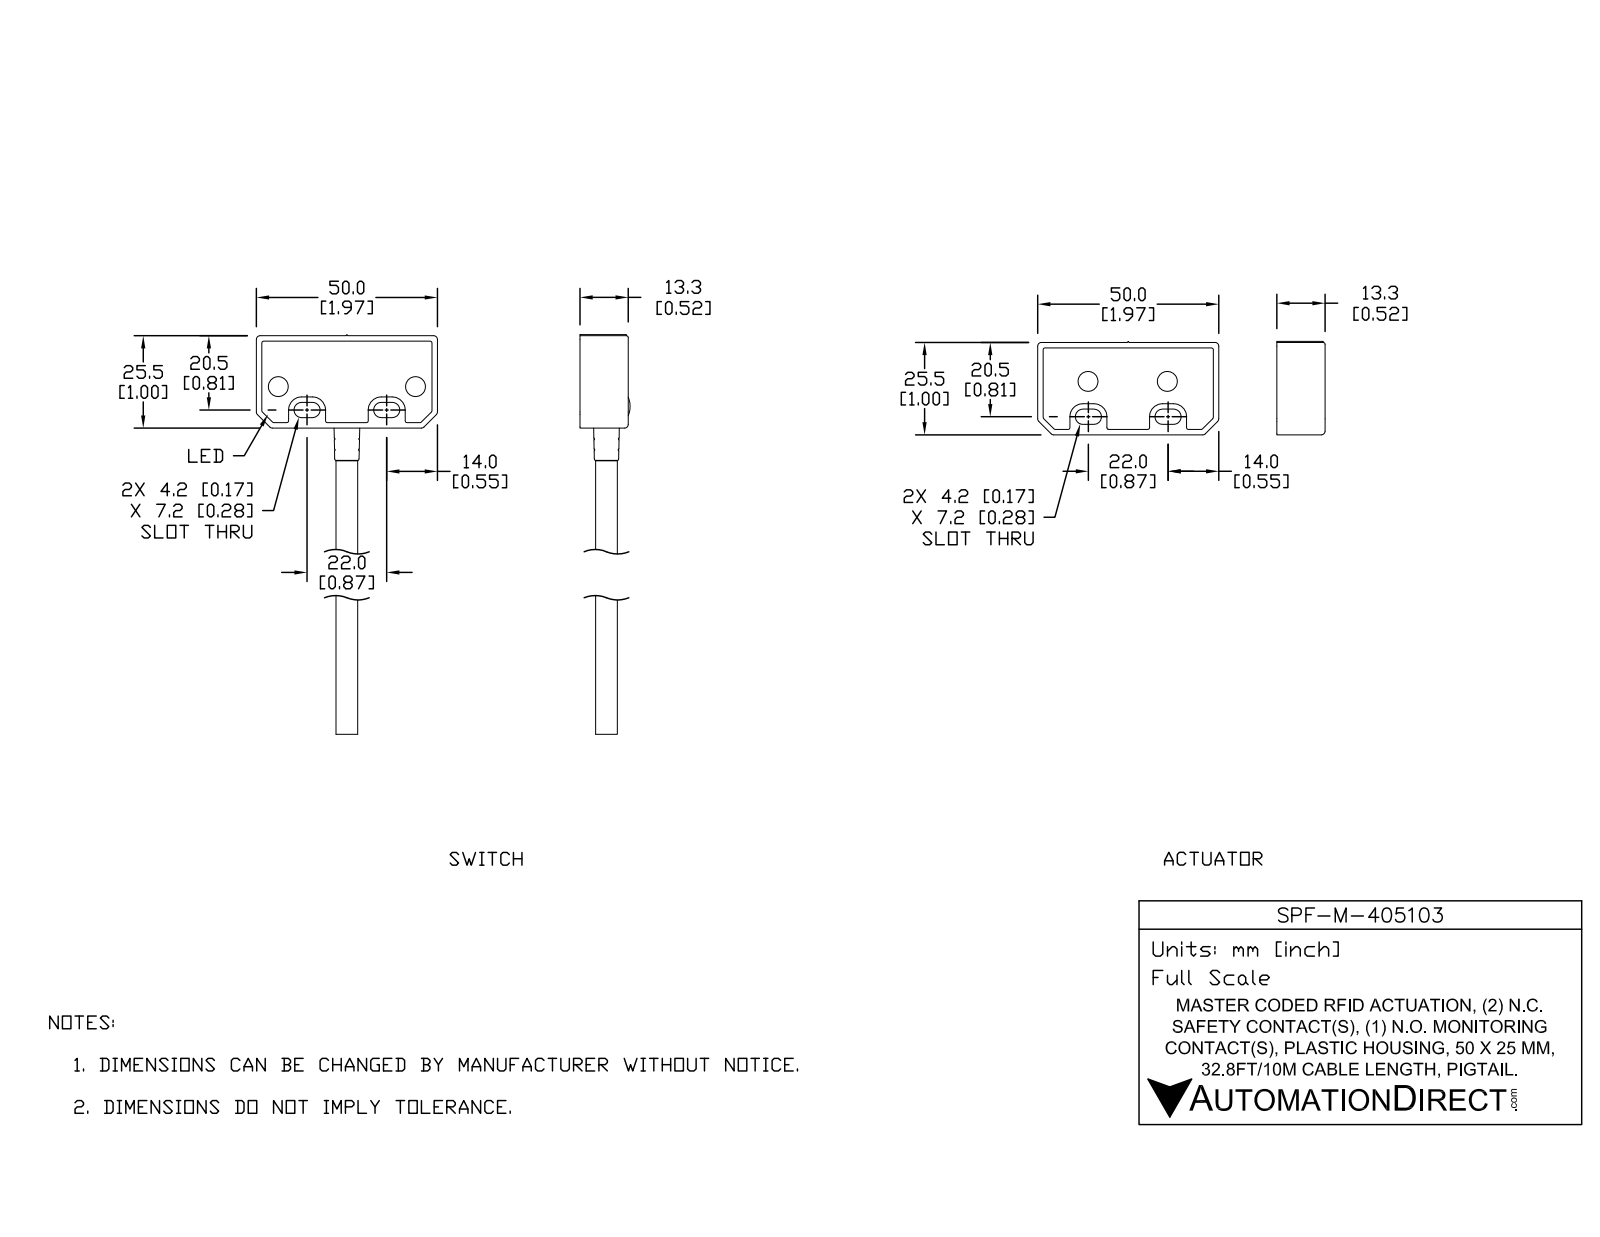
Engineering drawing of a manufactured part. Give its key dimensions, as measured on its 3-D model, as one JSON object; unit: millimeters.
{"part_name": "SPF-M-405103_2; SPF-M-405103; SPF-M-405103_1", "step_written_by": "SolidWorks 2017 (AUTOMOTIVE_DESIGN)", "units": "millimeters", "bodies": {"solids": 12, "faces": 1147, "planar": 475, "cylindrical": 358, "other": 314}, "overall_size": [205.5, 50, 13.8], "volume_mm3": 18110, "surface_area_mm2": 23430, "round_holes": [[5, 4], [3, 1], [4.4, 1], [5.4, 1], [5.9, 1], [7, 1]], "round_bosses_or_shafts": [[2, 4], [4.9, 2], [0.8, 2], [8.6, 1], [7.6, 1], [7.1, 1], [6, 1], [5.3, 1]], "partial_cylinders_radius": [[0.5, 132], [1, 36], [2, 8], [2.1, 8], [3.6, 8], [4.6, 8], [0.3, 6], [3.6, 4]], "face_to_face_distances": [1.5, 11.6, 10.1, 1.2, 11.3, 12.8, 26.5, 2.5, 24, 48.5], "hole_center_spacings": [5.6, 21.9, 27, 27.1, 32.6, 37.9, 39.4, 39.6]}
